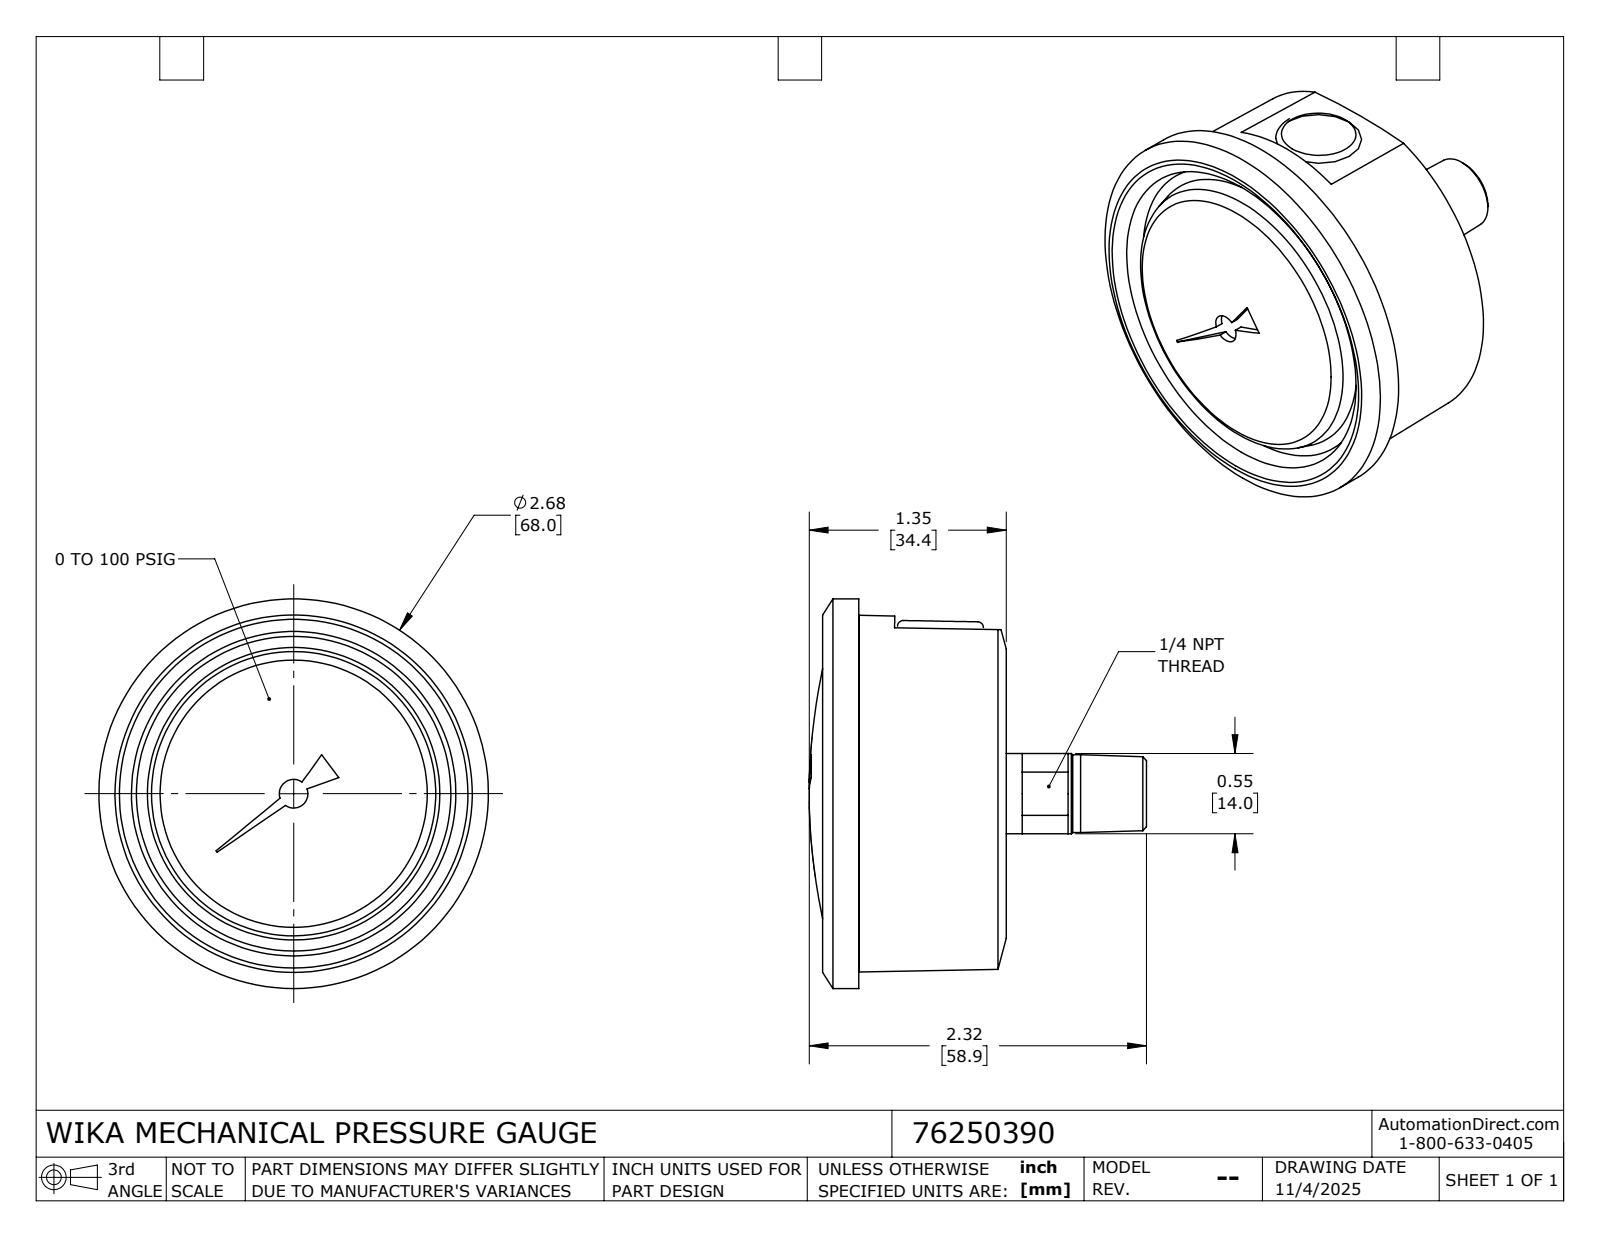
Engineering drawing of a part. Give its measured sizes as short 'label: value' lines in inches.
name: 76250390
written by: SolidWorks 2024 (CONFIG_CONTROL_DESIGN)
unit: in
bodies: 1 solid, 172 faces (62 planar, 54 cylindrical, 56 other)
size: 2.677 × 2.677 × 2.319
volume: 6.057 in³; area: 25.99 in²
holes: 1× ⌀0.118, 1× ⌀0.197, 1× ⌀0.709
bosses: 2× ⌀0.276, 1× ⌀2.677, 1× ⌀0.772, 1× ⌀0.551, 1× ⌀0.534, 1× ⌀0.157
rounds: 12× R0.012, 12× R0.028, 2× R0.371, 1× R0.313, 1× R0.532
face distances: 1.014, 0.126, 0.888, 1.078, 0.952, 0.064, 1.087, 0.961, 0.074, 1.262
